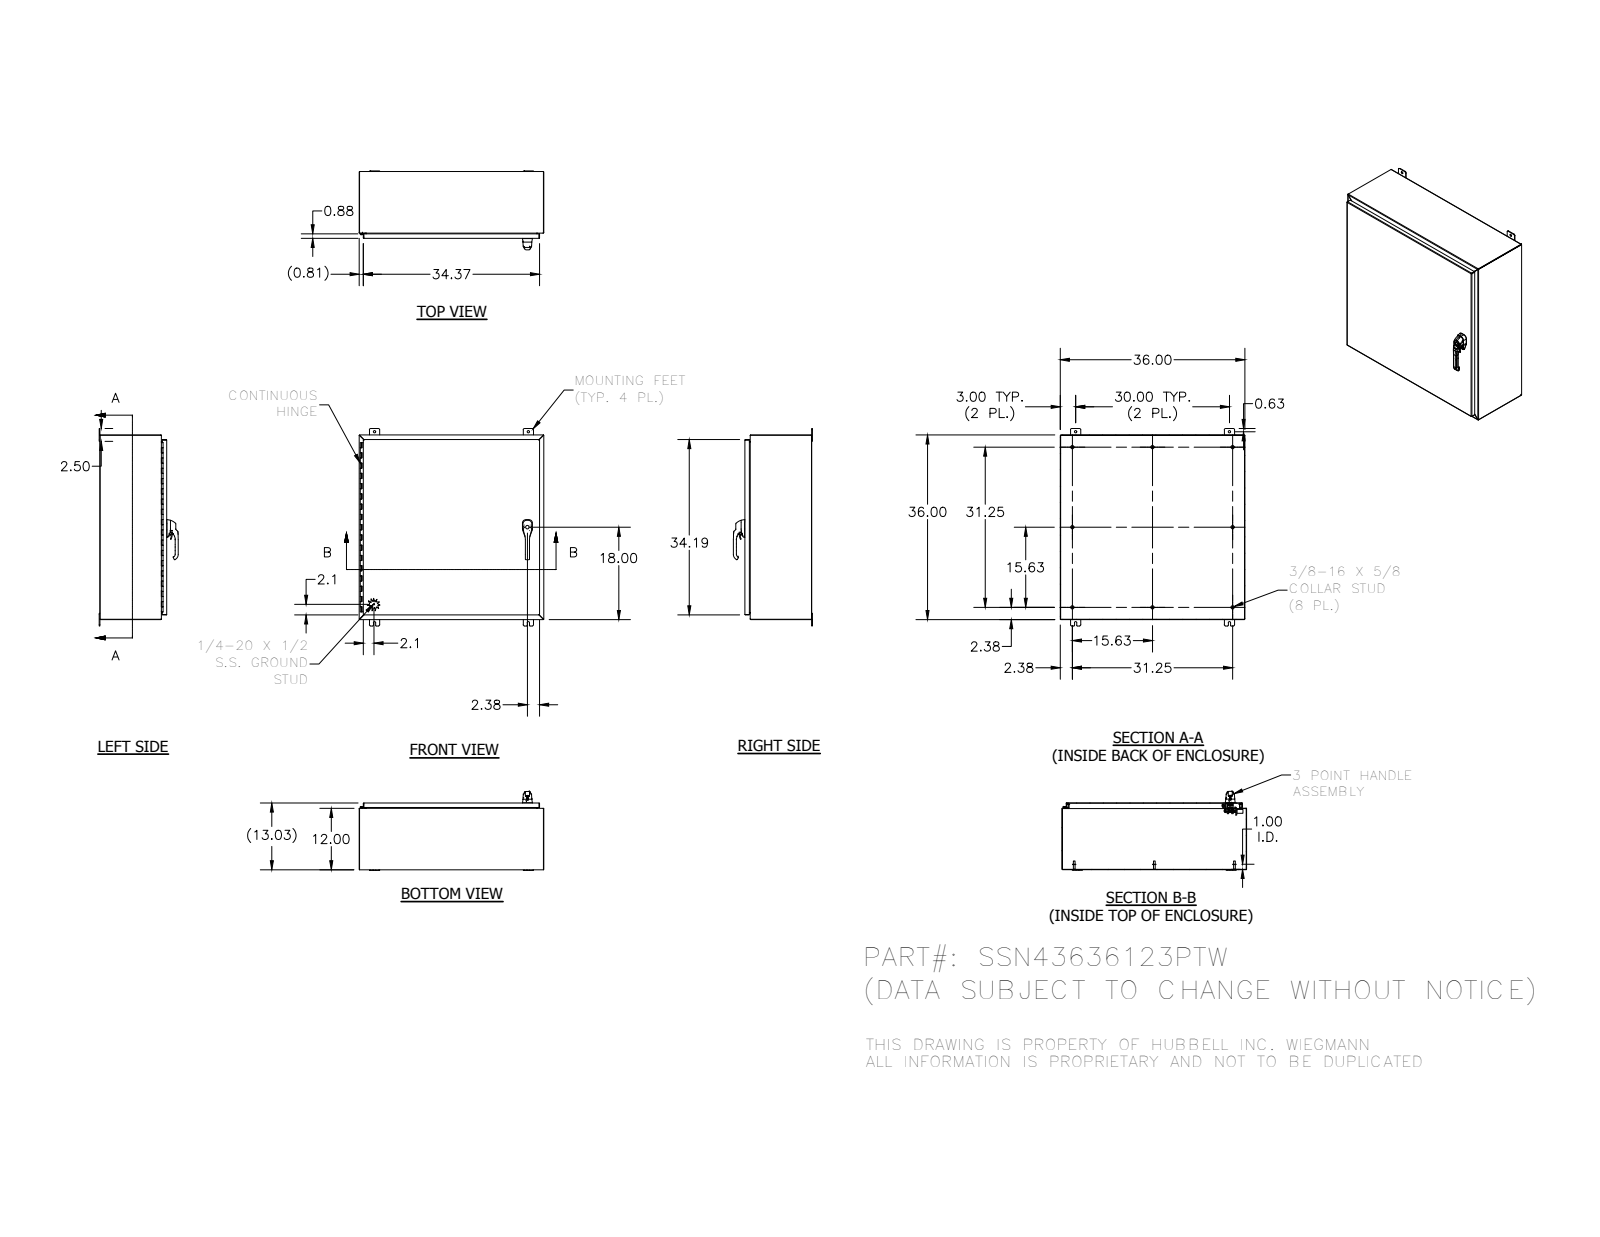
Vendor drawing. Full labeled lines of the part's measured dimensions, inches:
Part name (STEP PRODUCT): 1000-02; 1091-73; PLASTIC-ROLLER-CAM_AF0_ASM; SSN43636123PTW (+8 more)
STEP written by: SolidWorks 2014 (AUTOMOTIVE_DESIGN)
Units: inches
Bodies: 62 solids, 3213 faces (1120 planar, 1308 cylindrical, 785 other)
Overall size (bounding box): 38.5 × 36 × 15.408
Volume: 377.1 in³ · Surface area: 9 899 in²
Round holes (diameter × count): ⌀0.262 ×8, ⌀0.187 ×4, ⌀0.438 ×4, ⌀0.213 ×3, ⌀0.281 ×3, ⌀0.241 ×2, ⌀0.25 ×2, ⌀0.252 ×2, ⌀0.315 ×2, ⌀0.4 ×2, ⌀0.402 ×2, ⌀0.413 ×2
Round bosses / shafts (diameter × count): ⌀0.625 ×8, ⌀0.33 ×8, ⌀0.236 ×3, ⌀1 ×2, ⌀0.563 ×2, ⌀0.533 ×2, ⌀0.531 ×2, ⌀0.5 ×2
Partial cylindrical surfaces — rounded edges, fillets, slot ends (radius × count): R0.02 ×172, R0.012 ×113, R0.125 ×26, R0.031 ×22, R0.019 ×21, R0.25 ×20, R0.105 ×18, R0.05 ×15
Main face-to-face distances: 0.074, 12.959, 35.926, 12.885, 13.033, 35.852, 36, 11.926, 1.033, 12
Hole centre spacings: 0.38, 0.492, 0.76, 0.886, 26.428, 0.234, 0.258, 0.38
